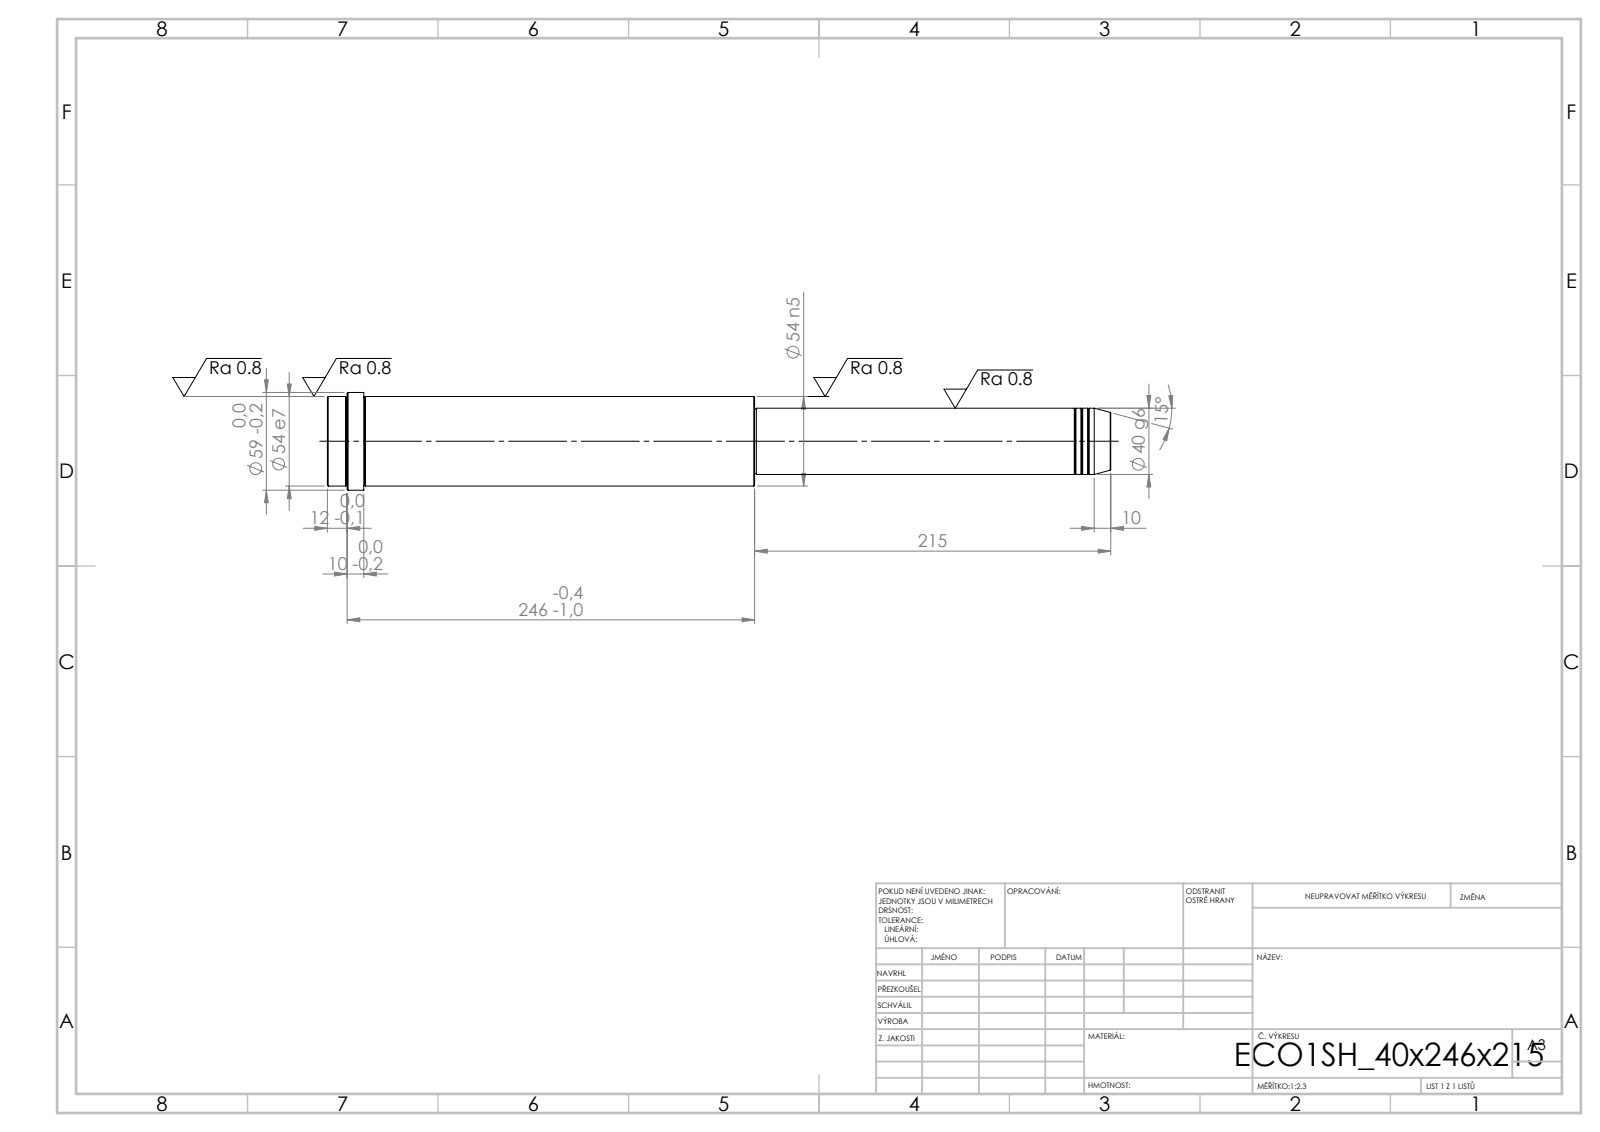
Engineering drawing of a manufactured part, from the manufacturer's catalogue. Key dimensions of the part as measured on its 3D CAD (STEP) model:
STEP written by: SolidWorks 2019 (CONFIG_CONTROL_DESIGN)
Units: millimetres
Bodies: 1 solid, 52 faces (6 planar, 16 cylindrical, 30 other)
Overall size (bounding box): 473 × 59 × 59
Volume: 863 474 mm³ · Surface area: 76 402 mm²
Round bosses / shafts (diameter × count): ⌀59 ×1, ⌀54 ×1, ⌀40 ×1, ⌀39 ×1
Main face-to-face distances: 258, 215, 473, 451, 236, 22, 461, 246, 10, 12
